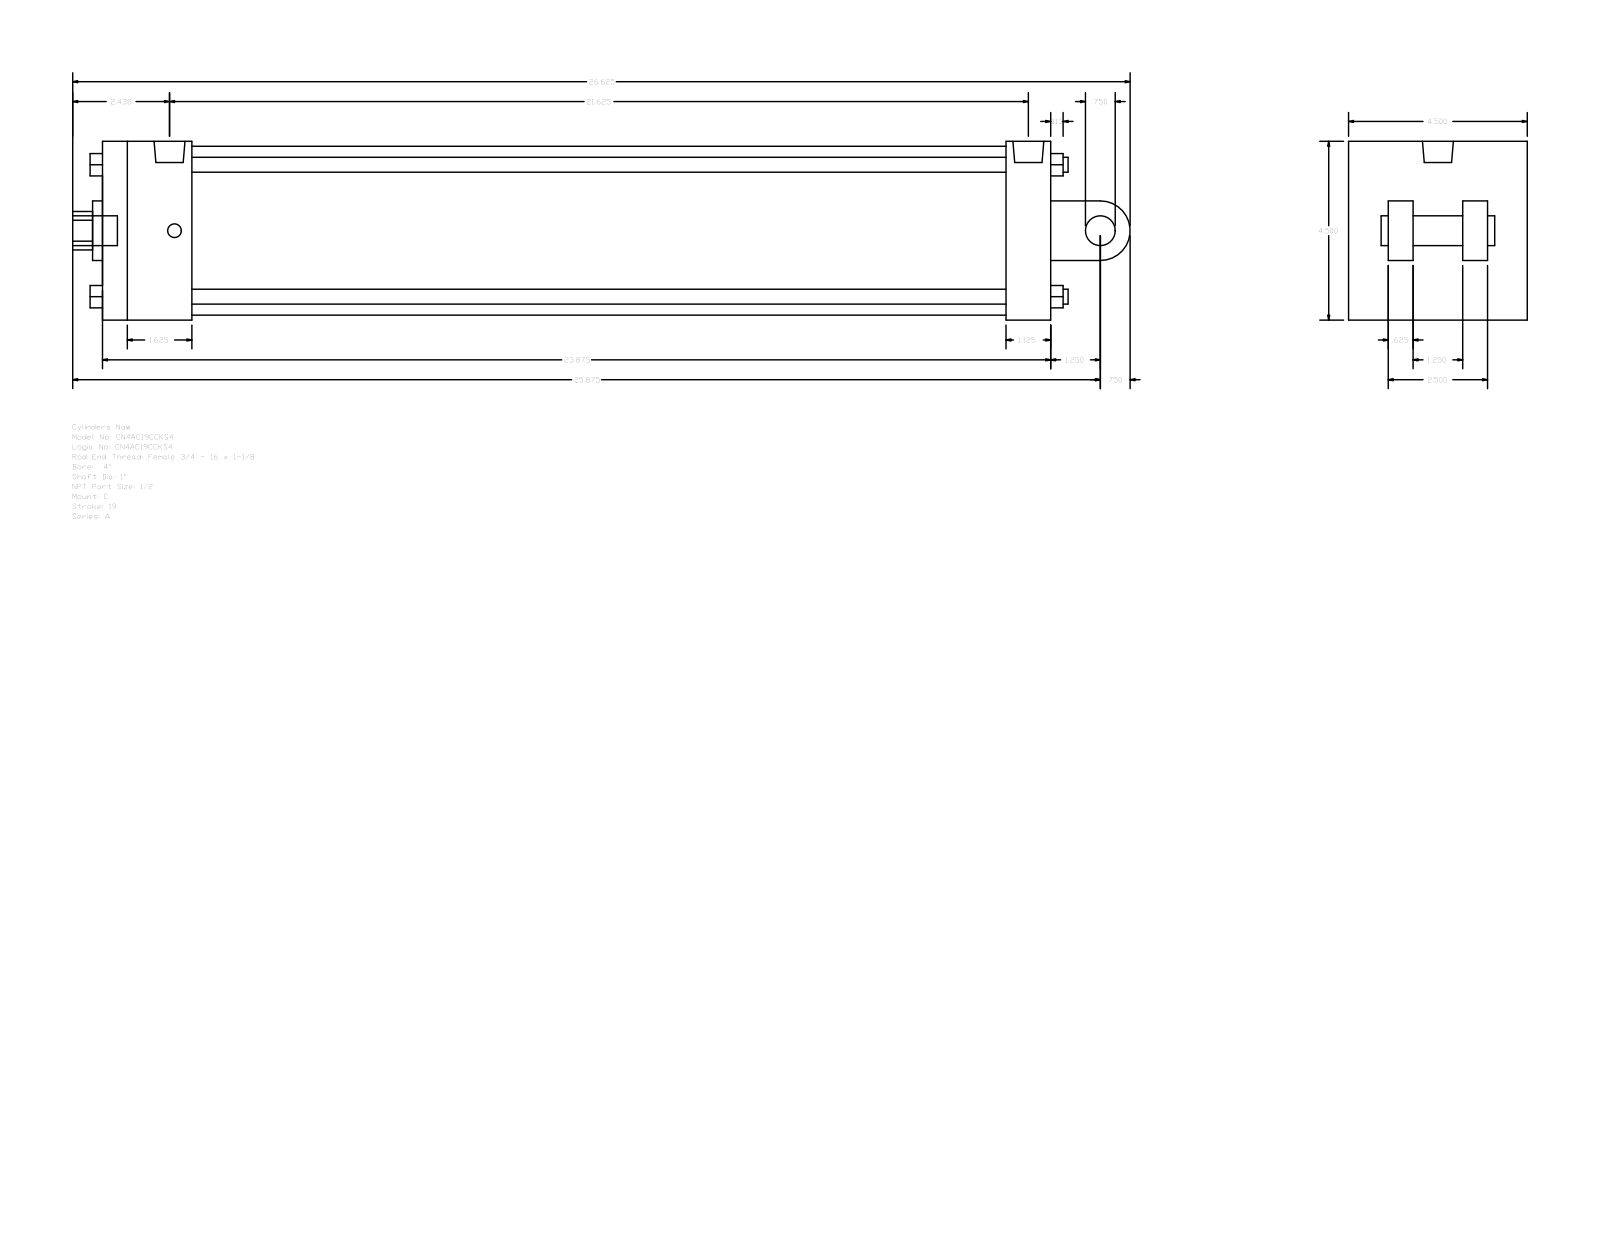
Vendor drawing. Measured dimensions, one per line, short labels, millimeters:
name: A_C__0400_1
written by: GSSL Pune (CONFIG_CONTROL_DESIGN)
unit: mm
bodies: 0 solids, 135 faces (102 planar, 33 cylindrical, 0 other)
size: 676.27 × 114.3 × 114.3
holes: 2× ⌀8.73, 1× ⌀19.77, 1× ⌀25.4, 1× ⌀38.1, 1× ⌀107.95
bosses: 4× ⌀9.53, 2× ⌀19.05, 2× ⌀8.73, 1× ⌀19.77
rounds: 1× R12.29, 1× R19.05
face distances: 114.3, 606.43, 73.03, 577.85, 28.58, 57.15, 520.7, 549.28, 15.87, 47.63
hole spacings: 3.18
